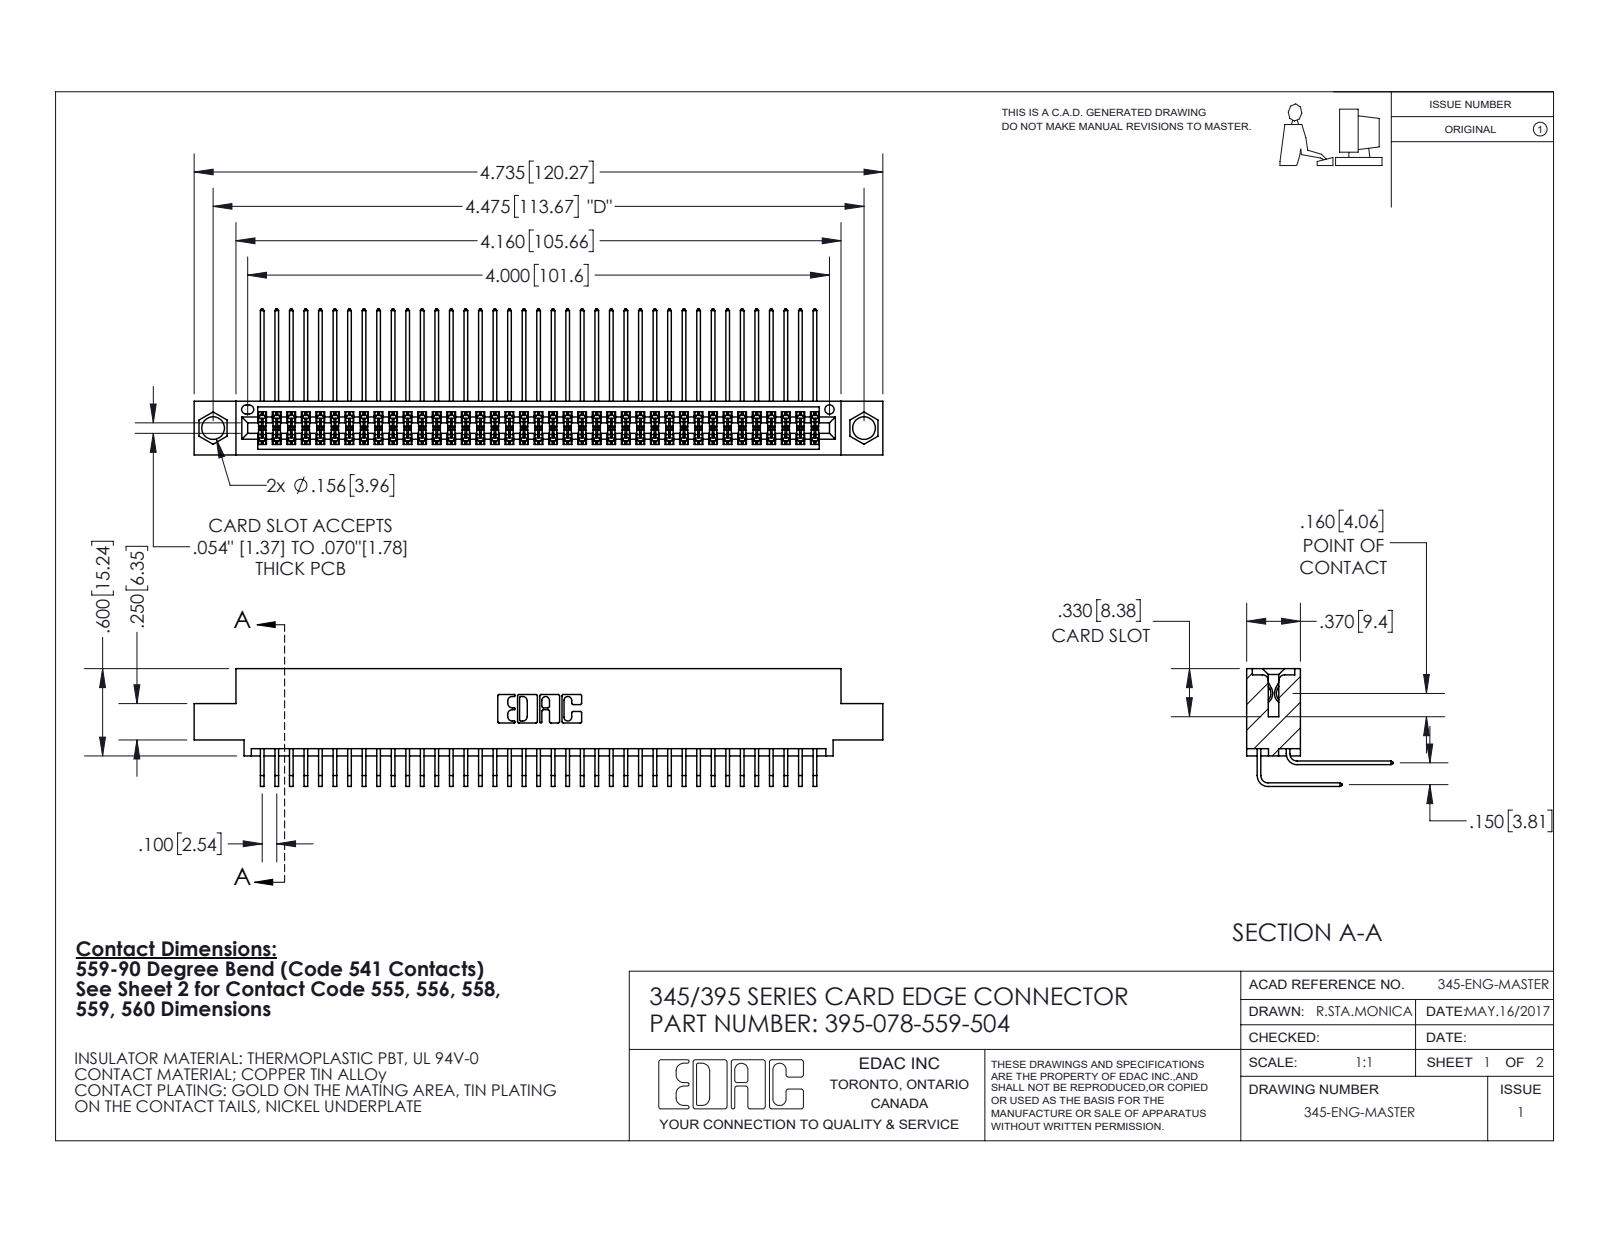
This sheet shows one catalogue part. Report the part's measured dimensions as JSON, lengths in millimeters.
{"part_name": "345-292-001_559 Tail - 2; 395-078-559-504; 345-292-001_558 559 Tail - 1; 345 Part_0.110 Offset - 0.156 Dia-TI", "step_written_by": "SolidWorks 2020 (CONFIG_CONTROL_DESIGN)", "units": "millimeters", "bodies": {"solids": 79, "faces": 4200, "planar": 2828, "cylindrical": 1372, "other": 0}, "overall_size": [120.3, 25.5, 20.5], "volume_mm3": 11900, "surface_area_mm2": 19630, "round_holes": [[4, 2], [1.6, 1]], "partial_cylinders_radius": [[0.2, 117], [0.3, 22], [0.2, 6], [0.8, 6], [0.7, 3], [0.4, 2], [0.5, 2], [0.6, 2]], "face_to_face_distances": [1.8, 7.6, 5.1, 9.4, 2.5, 6.9, 0.6, 5.7, 4.4, 3.8], "hole_center_spacings": [6.9, 107.7, 113.7]}
